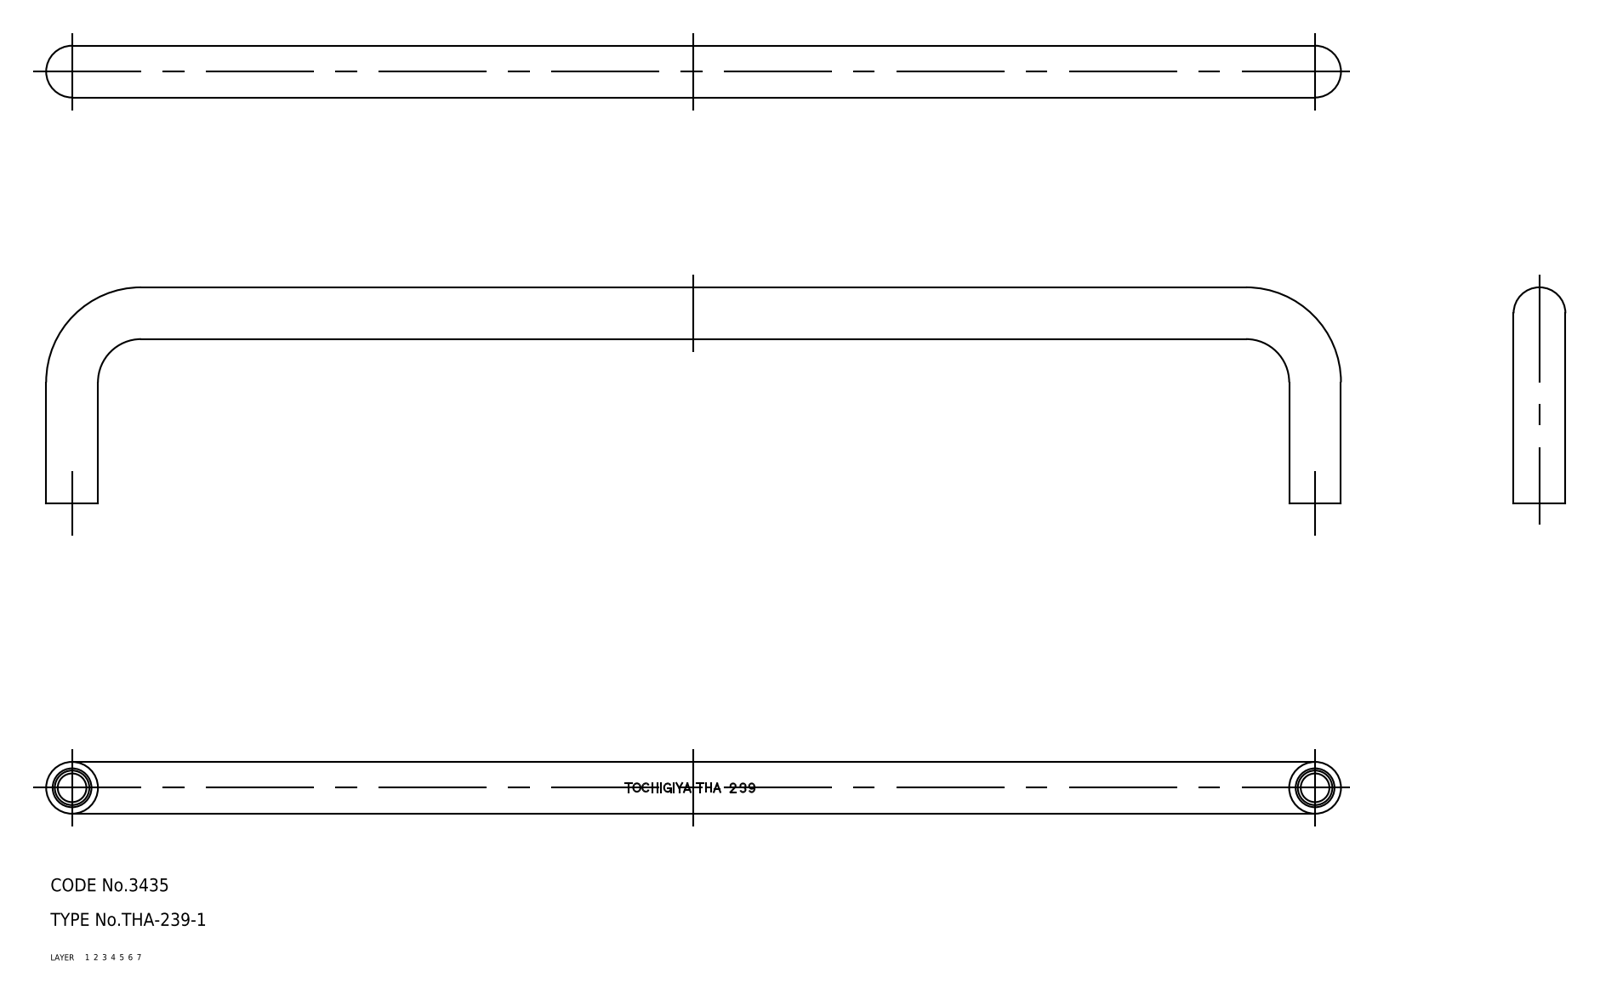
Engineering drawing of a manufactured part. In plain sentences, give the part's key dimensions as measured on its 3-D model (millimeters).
The part is named "pull". Its 3-D file was written by "CADfix (AUTOMOTIVE_DESIGN)". It is 1 solid with 18 faces: 0 planar, 0 cylindrical and 18 other. Overall it measures 300 by 50 by 12 millimeters. Its volume is 40 031 cubic millimeters and its surface area 14 396 square millimeters.
